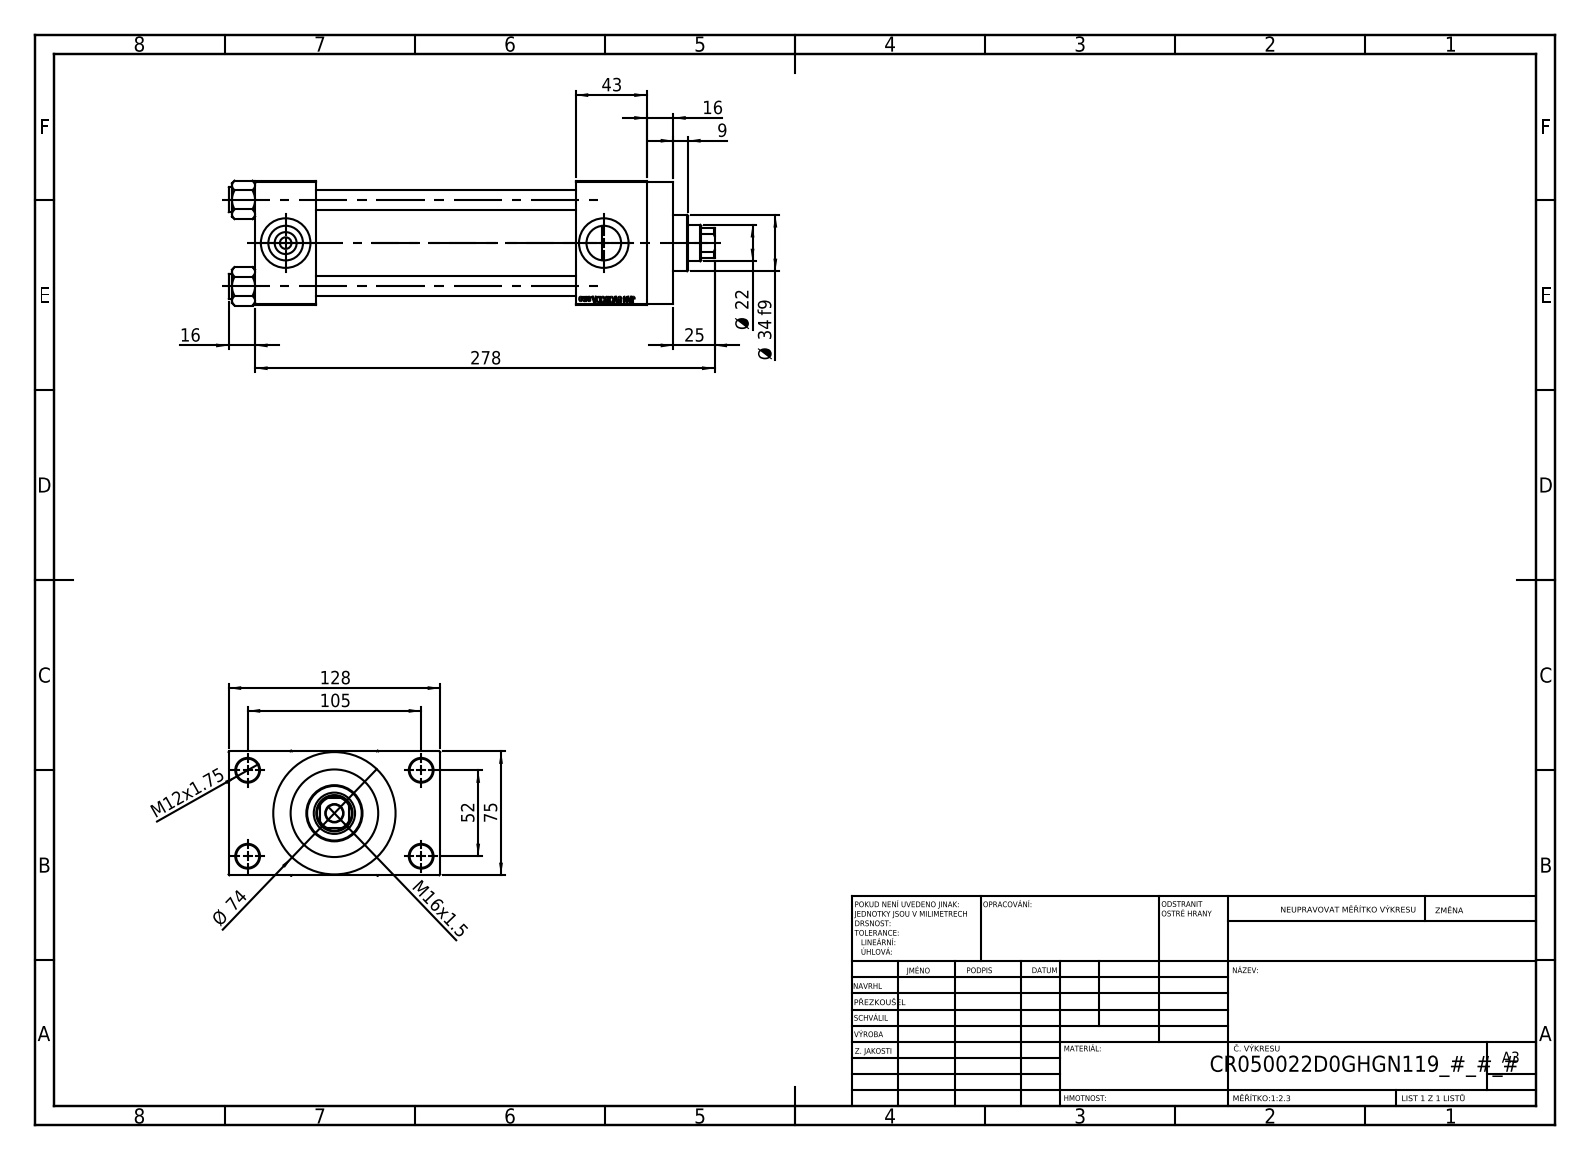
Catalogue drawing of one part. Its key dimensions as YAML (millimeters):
part_name: "NUT_M5_D; V215_VC_A; V215CR_D_Body; V215CR_VCP_D (+1 more)"
step_written_by: "SolidWorks 2019 (CONFIG_CONTROL_DESIGN)"
units: millimeters
bodies: {solids: 11, faces: 1103, planar: 497, cylindrical: 88, other: 518}
overall_size: [294, 128, 75.54]
volume: 929390
surface_area: 221426
round_holes:
  - {diameter: 12, count: 4}
  - {diameter: 14, count: 4}
  - {diameter: 7, count: 2}
  - {diameter: 20.96, count: 2}
  - {diameter: 30, count: 2}
  - {diameter: 10.5, count: 1}
  - {diameter: 22, count: 1}
  - {diameter: 25, count: 1}
  - {diameter: 41, count: 1}
  - {diameter: 50, count: 1}
  - {diameter: 53, count: 1}
round_bosses_or_shafts:
  - {diameter: 15, count: 4}
  - {diameter: 74, count: 1}
  - {diameter: 56, count: 1}
  - {diameter: 34, count: 1}
partial_cylinders:
  - {radius: 10.5, count: 1}
face_to_face_distances: [75, 157, 37, 194, 26.5, 237, 200, 43, 101.5, 16]
hole_center_spacings: [26.35, 36.98, 52.3, 58.43, 58.59, 78.65, 94.37, 52]
